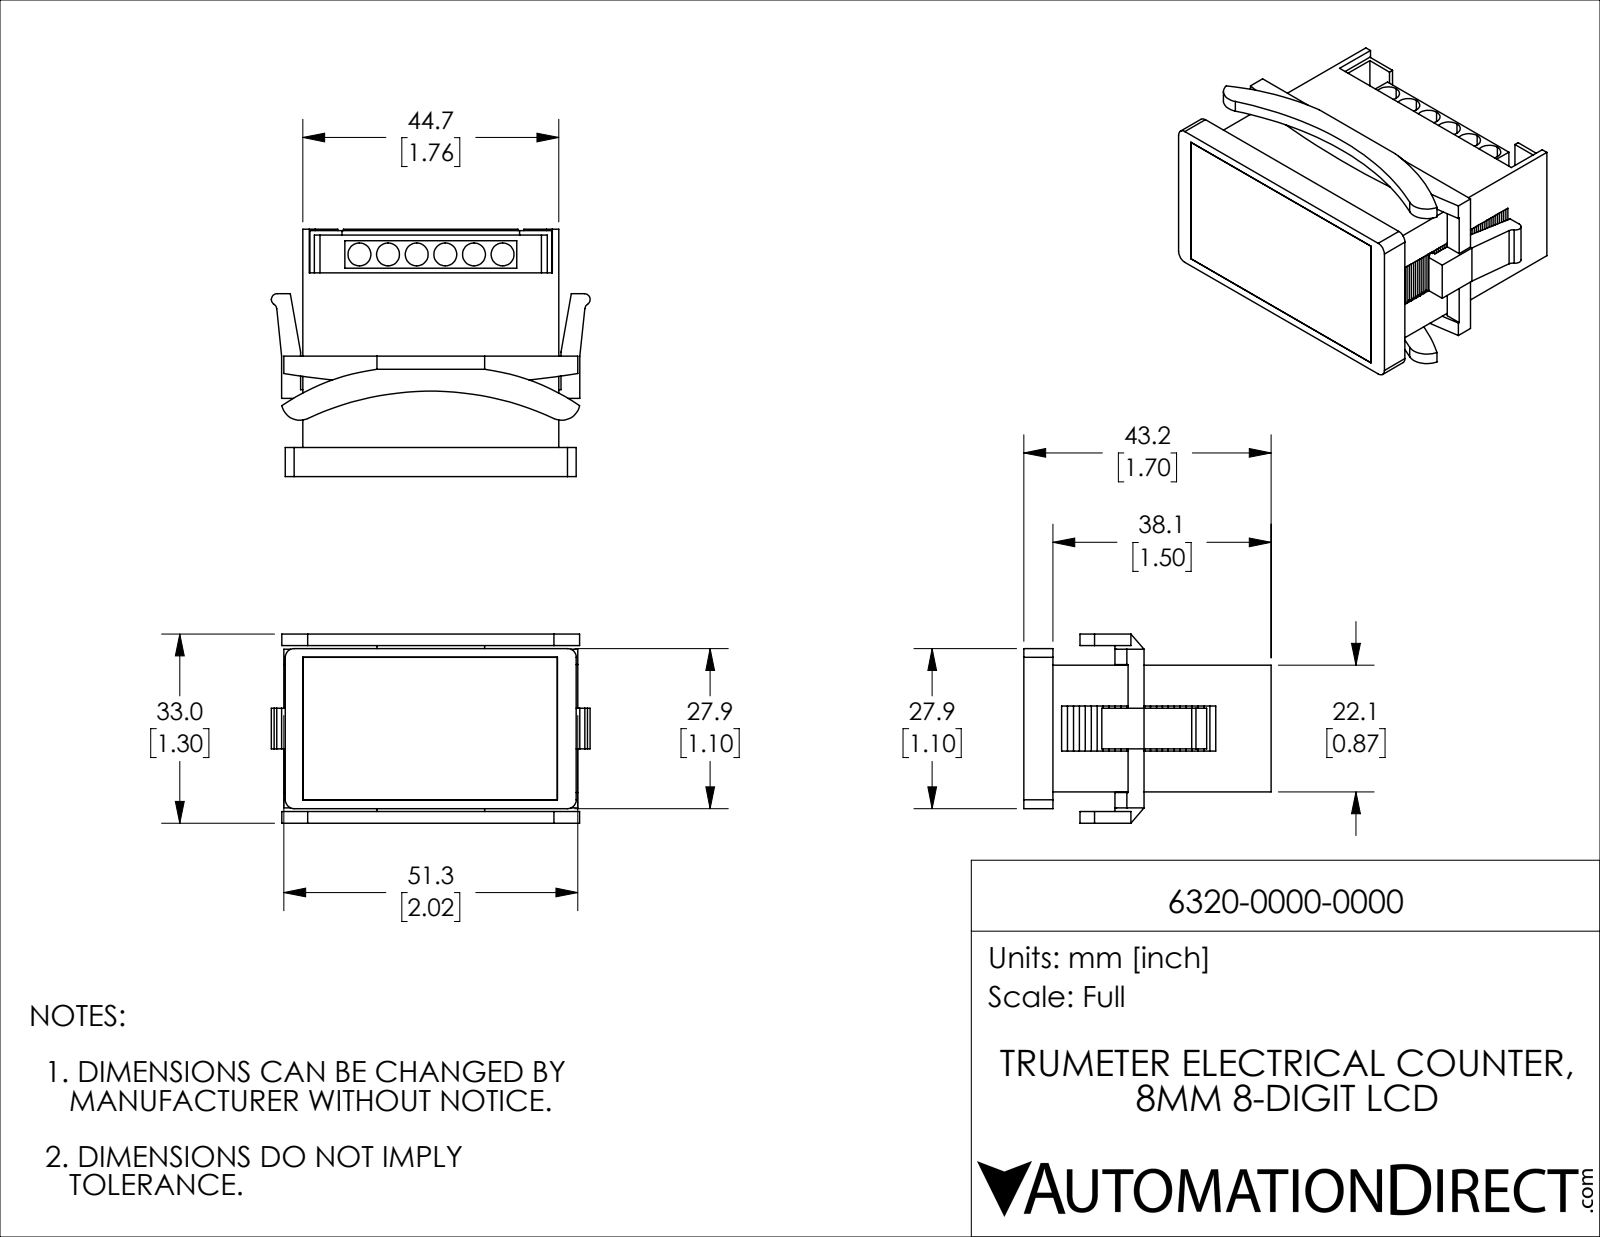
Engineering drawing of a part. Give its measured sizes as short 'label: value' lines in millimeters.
name: 6320-0000-0000
written by: SolidWorks 2021 (CONFIG_CONTROL_DESIGN)
unit: mm
bodies: 6 solids, 464 faces (431 planar, 33 cylindrical, 0 other)
size: 55.66 × 43.18 × 33.02
volume: 22 821 mm³; area: 31 399 mm²
holes: 6× ⌀4
rounds: 4× R1.02, 4× R1.52, 2× R3.2, 2× R38.1, 1× R50.8, 1× R159.51
face distances: 1.14, 2, 20.96, 0.86, 0.76, 1.24, 1.02, 1.52, 22.1, 20.1
hole spacings: 5, 10, 15, 20, 25
